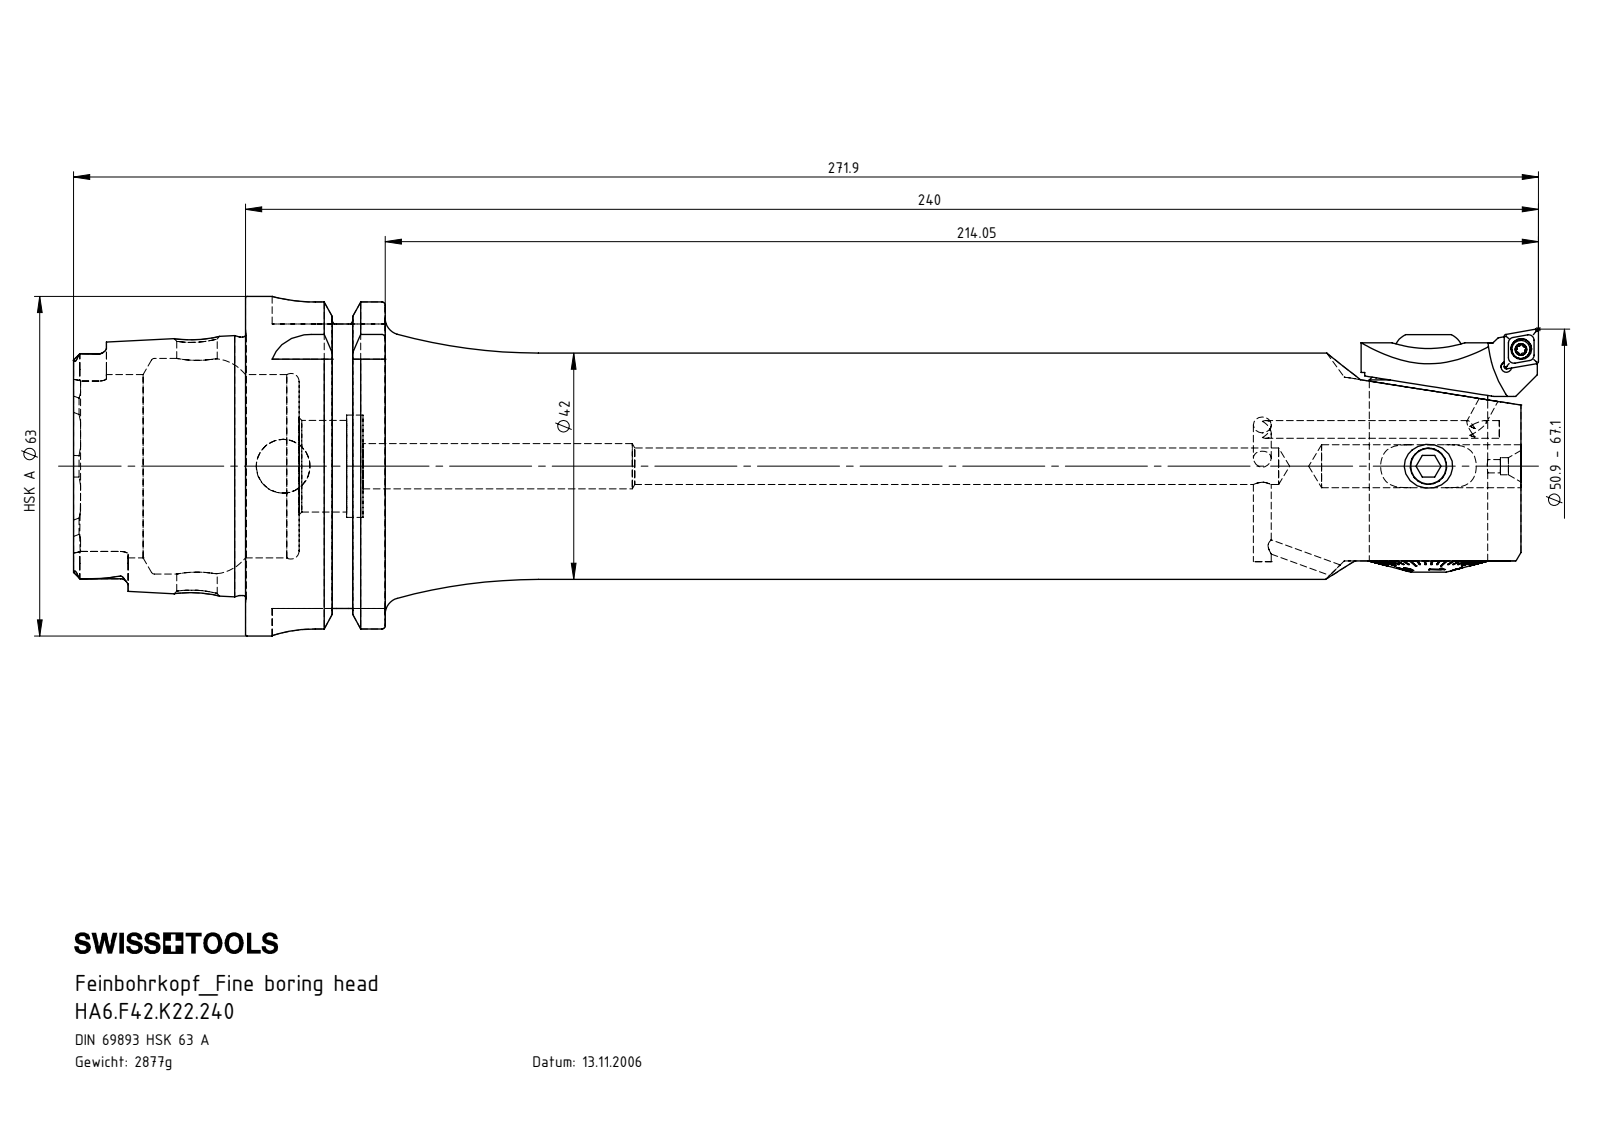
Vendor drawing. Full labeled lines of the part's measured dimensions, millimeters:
Part name (STEP PRODUCT): F42-WCA.001.009; F42-BG3.002.024_A; WCA-ER2.001.006_A; HA6-F42.K20.240_B_Fertigbearbeitung (+8 more)
STEP written by: SolidWorks 2022 (CONFIG_CONTROL_DESIGN)
Units: millimetres
Bodies: 11 solids, 846 faces (352 planar, 174 cylindrical, 320 other)
Overall size (bounding box): 271.9 × 63 × 63
Volume: 362 954 mm³ · Surface area: 66 393 mm²
Round holes (diameter × count): ⌀3.3 ×4, ⌀2.5 ×3, ⌀1.9 ×2, ⌀6.8 ×2, ⌀0.8 ×1, ⌀2.05 ×1, ⌀2.1 ×1, ⌀2.8 ×1, ⌀3.2 ×1, ⌀3.85 ×1, ⌀5.75 ×1, ⌀7.5 ×1
Round bosses / shafts (diameter × count): ⌀63 ×1, ⌀54.95 ×1, ⌀47.94 ×1, ⌀42 ×1, ⌀22.3 ×1, ⌀18.45 ×1, ⌀13.9 ×1, ⌀13 ×1
Partial cylindrical surfaces — rounded edges, fillets, slot ends (radius × count): R0.21 ×6, R1.4 ×6, R0.36 ×4, R0.5 ×4, R2.88 ×4, R8 ×4, R0.36 ×2, R2 ×2
Main face-to-face distances: 236.75, 16, 25.95, 210.8, 9.95, 226.8, 31.9, 8.85, 41.85, 57.85
Hole centre spacings: 1, 3.83, 3.98, 7.67, 10.5, 13.2, 15.58, 16.87
